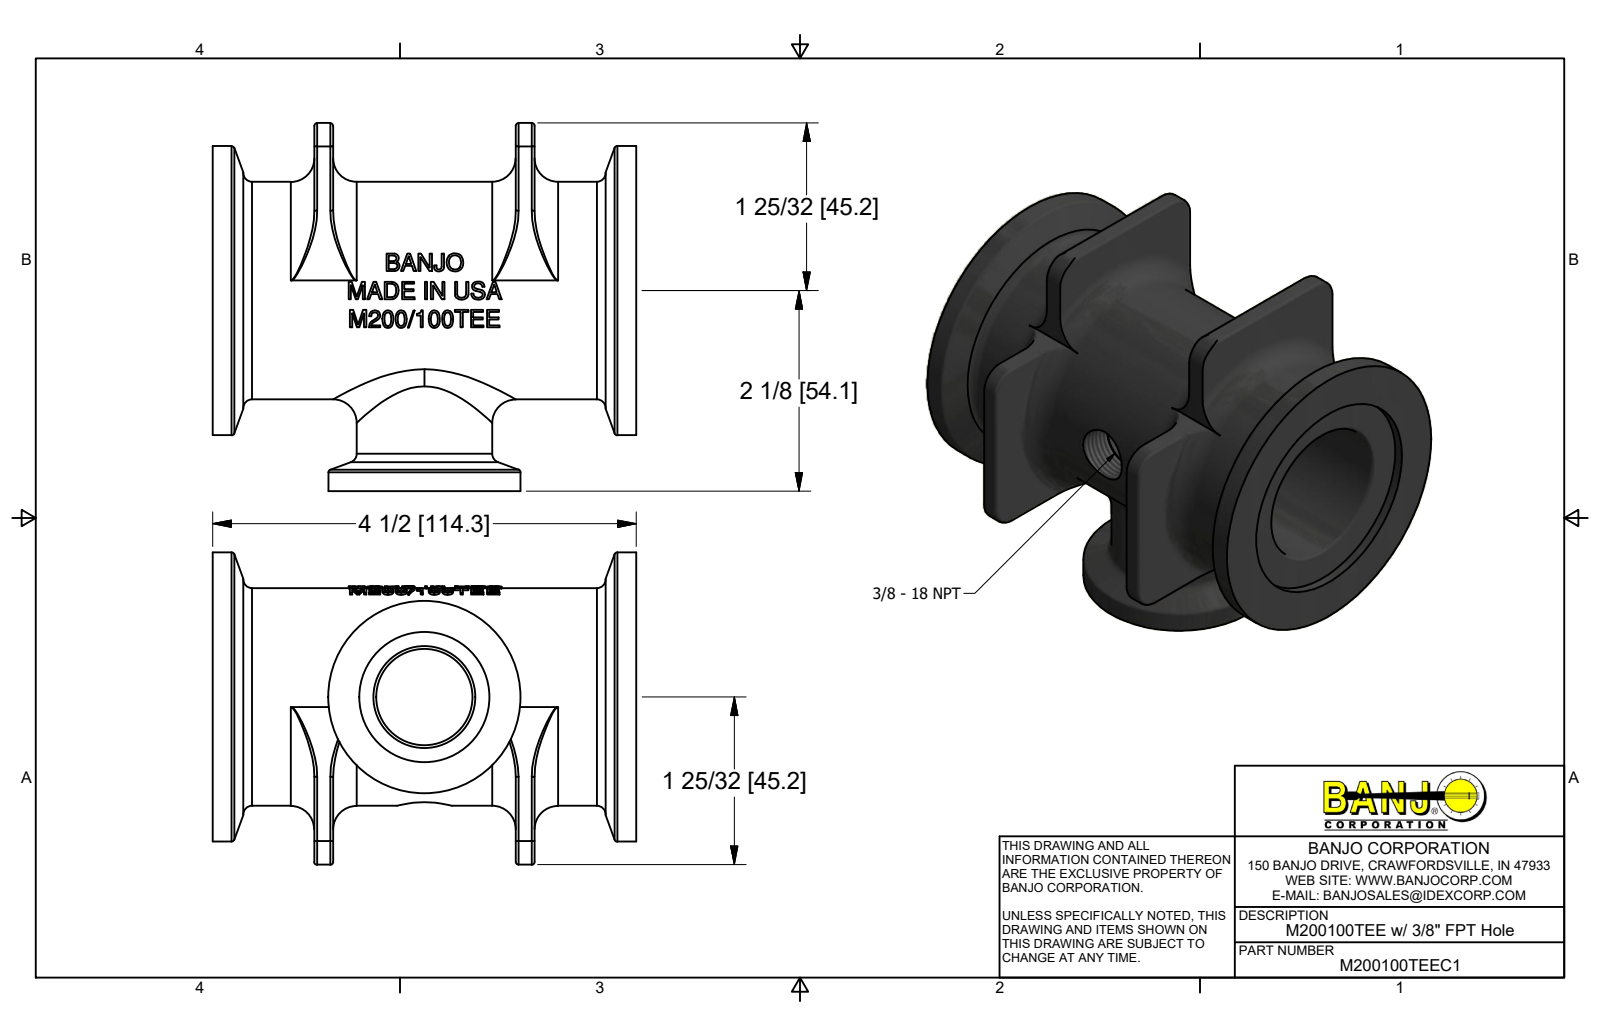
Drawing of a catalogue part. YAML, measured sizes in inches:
part_name: "M200100TEEC1; M200100TEE"
step_written_by: "Autodesk Inventor 2017 (AUTOMOTIVE_DESIGN)"
units: inches
bodies: {solids: 1, faces: 436, planar: 203, cylindrical: 81, other: 152}
overall_size: [4.5, 3.91, 3.315]
volume: 14.72
surface_area: 94.62
round_holes:
  - {diameter: 0.547, count: 1}
  - {diameter: 1.02, count: 1}
  - {diameter: 1.38, count: 1}
  - {diameter: 1.5, count: 1}
  - {diameter: 2.19, count: 1}
round_bosses_or_shafts:
  - {diameter: 3.07, count: 1}
  - {diameter: 2.31, count: 1}
  - {diameter: 2.04, count: 1}
  - {diameter: 1.44, count: 1}
partial_cylinders:
  - {radius: 0.03, count: 20}
  - {radius: 0.25, count: 4}
  - {radius: 1.175, count: 1}
face_to_face_distances: [0.98, 0.1, 4.4, 4.5, 2.14, 1.08, 3.42, 3.32, 1.28, 3.22]
